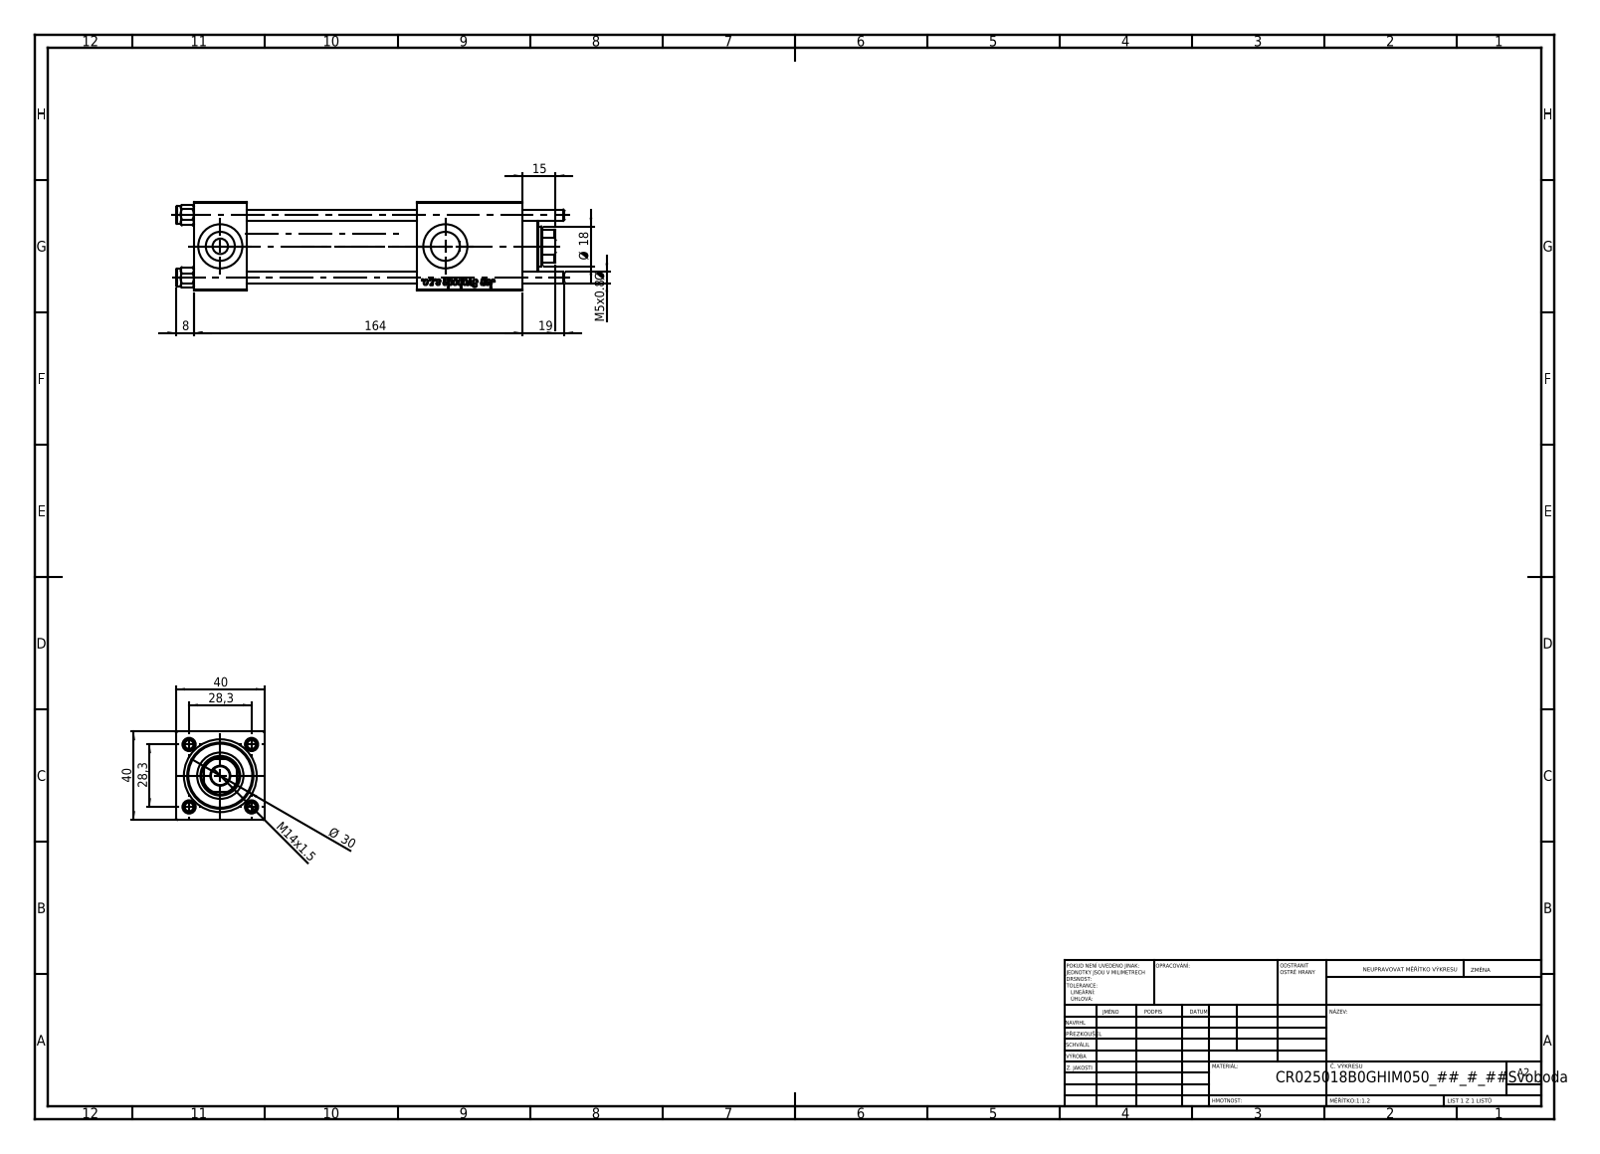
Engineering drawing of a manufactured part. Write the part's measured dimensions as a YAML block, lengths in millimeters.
part_name: "V215CR_B_TYCINKA; V215CR_VCP_B; V215_VC_A; NUT_M5_B (+1 more)"
step_written_by: "SolidWorks 2019 (CONFIG_CONTROL_DESIGN)"
units: millimeters
bodies: {solids: 11, faces: 1152, planar: 428, cylindrical: 76, other: 648}
overall_size: [176, 40, 40]
volume: 170398
surface_area: 69754
round_holes:
  - {diameter: 5, count: 4}
  - {diameter: 20, count: 3}
  - {diameter: 7, count: 2}
  - {diameter: 13.16, count: 2}
  - {diameter: 8.5, count: 1}
  - {diameter: 18, count: 1}
  - {diameter: 21, count: 1}
  - {diameter: 25, count: 1}
  - {diameter: 30, count: 1}
round_bosses_or_shafts:
  - {diameter: 8, count: 4}
  - {diameter: 31, count: 1}
partial_cylinders:
  - {radius: 8.5, count: 1}
face_to_face_distances: [40, 24, 101, 77, 120.3, 96.3, 19.3, 149, 125, 48]
hole_center_spacings: [20.01, 28.3, 40.02, 102]
